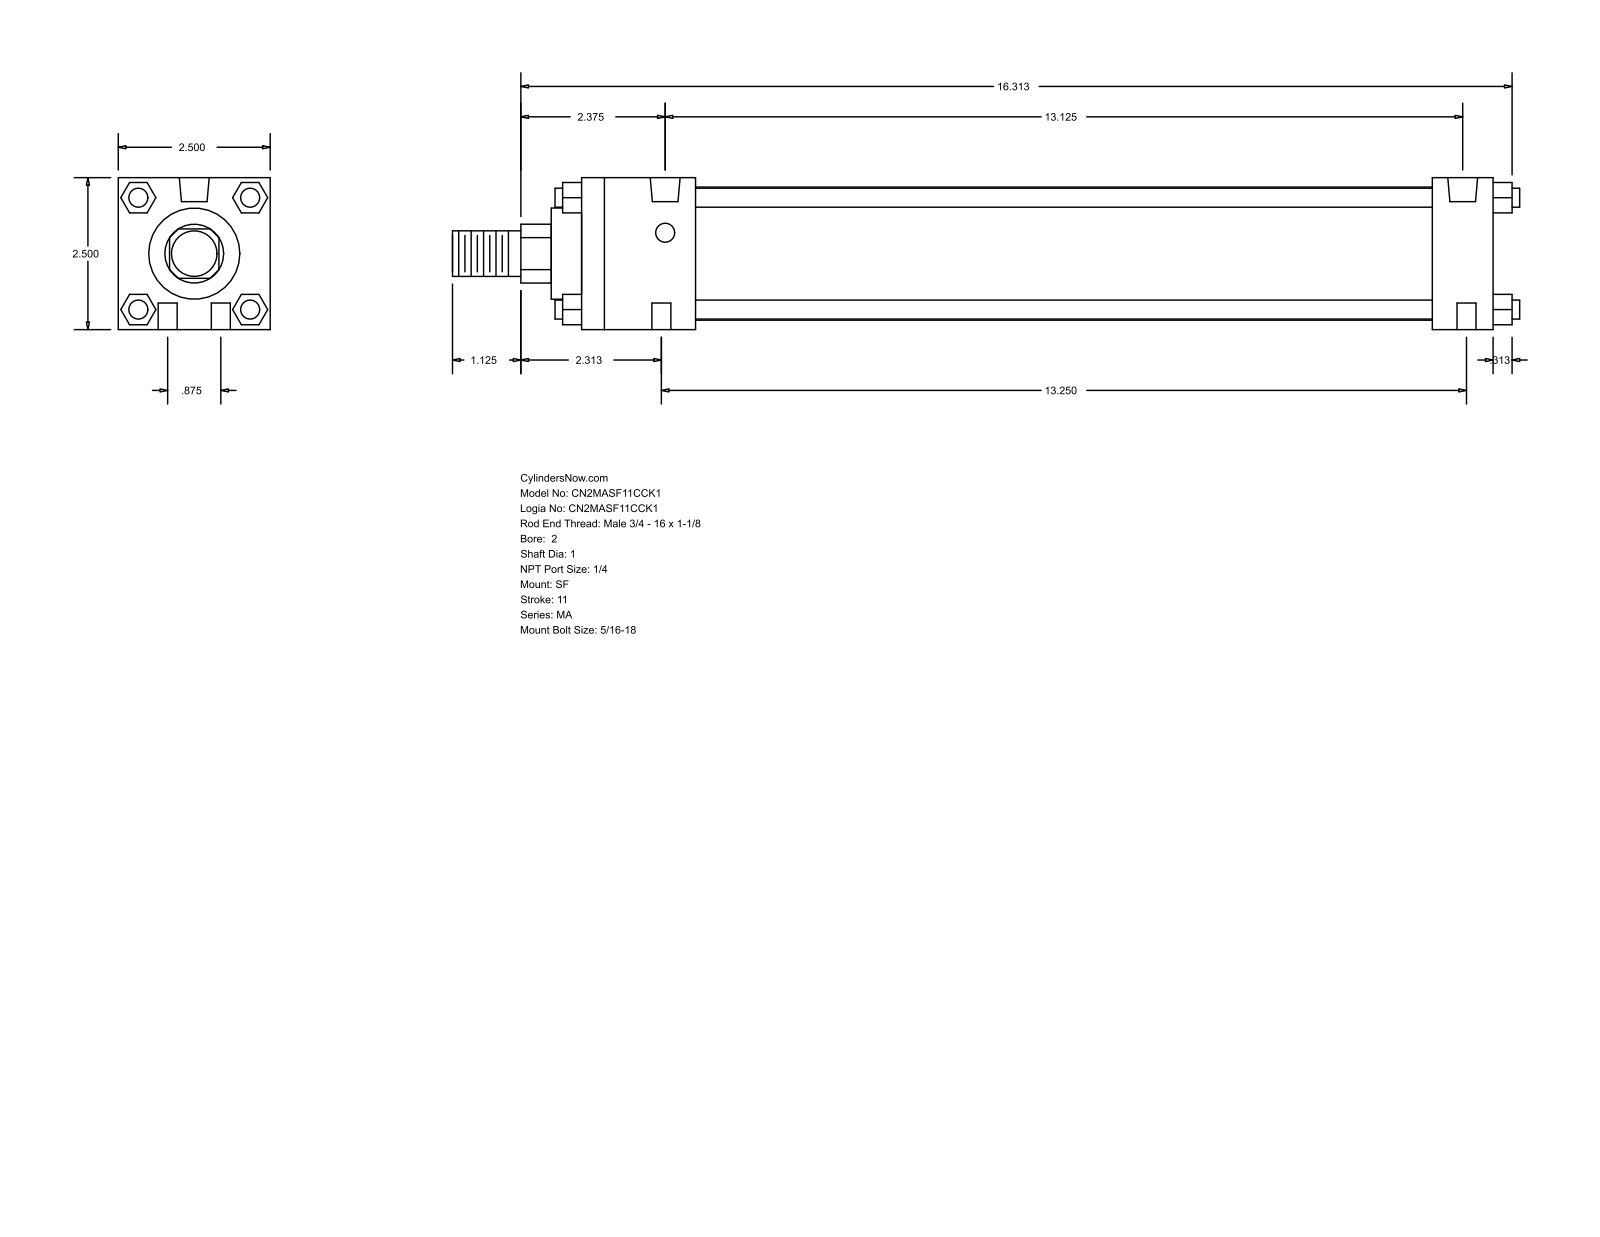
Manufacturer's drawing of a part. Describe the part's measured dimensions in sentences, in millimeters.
The part is named "MA_SF__0200_1". Its 3-D file was written by "GSSL Pune (CONFIG_CONTROL_DESIGN)". It is 0 solids with 124 faces: 94 planar, 30 cylindrical and 0 other. Overall it measures 446.09 by 63.5 by 63.5 millimeters. Round holes: 6 of diameter 7.94, 2 of diameter 12.49. Round bosses or shafts: 4 of diameter 7.94, 1 of diameter 55.63, 1 of diameter 38.1, 1 of diameter 25.4, 1 of diameter 19.05. Partial cylindrical surfaces (rounded edges, fillets, slot ends): 1 of radius 12.29. The main face-to-face distances are 63.5, 381, 12.7, 25.4, 355.6, 47.63, 307.97, 333.37, 40.47, 23.37. The hole center spacings are 11.22, 335.14, 22.22, 333.37, 336.55, 337.28.
